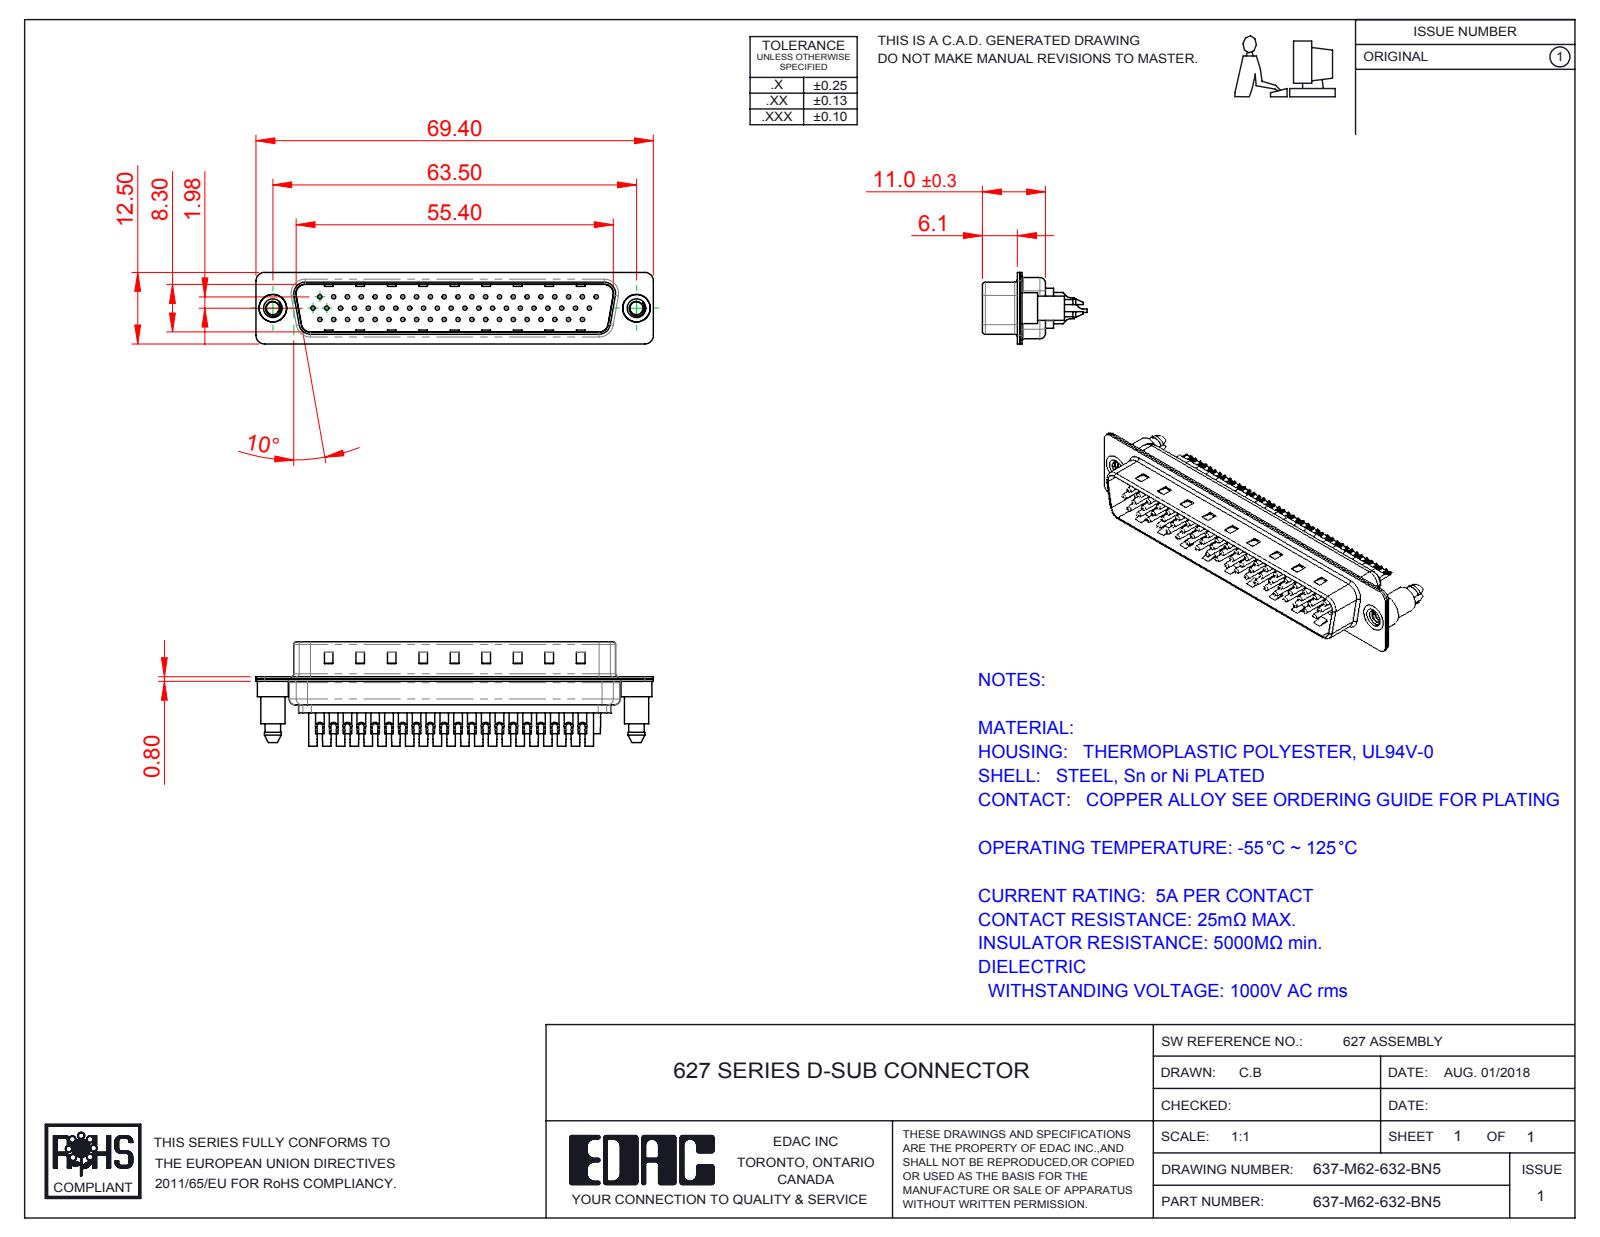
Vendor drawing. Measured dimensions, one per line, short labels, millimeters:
name: 637M Shell Rear_62 Contacts; 637M Contact Row 3_32; 637M Contact Row 2_32; 637M Shell Front_62 Contacts (+4 more)
written by: SolidWorks 2016 (CONFIG_CONTROL_DESIGN)
unit: mm
bodies: 67 solids, 2756 faces (777 planar, 1165 cylindrical, 814 other)
size: 69.4 × 18.25 × 12.5
volume: 4 256 mm³; area: 12 510 mm²
holes: 62× ⌀0.75, 62× ⌀1, 62× ⌀1.6, 62× ⌀2, 2× ⌀2.26, 2× ⌀4, 2× ⌀4.8
bosses: 62× ⌀1.5, 2× ⌀5.4, 2× ⌀4.9, 2× ⌀4.25
rounds: 18× R1.5, 12× R2, 10× R1.6, 8× R0.5, 7× R1, 4× R0.25, 4× R0.6, 4× R0.65
face distances: 0.4, 0.8, 9.5, 9.1, 8.7, 9.9, 0.75, 0.35, 1.2, 1.9
hole spacings: 7.24, 2.32, 2.41, 4.13, 9.65, 4.83, 14.48, 11.04
